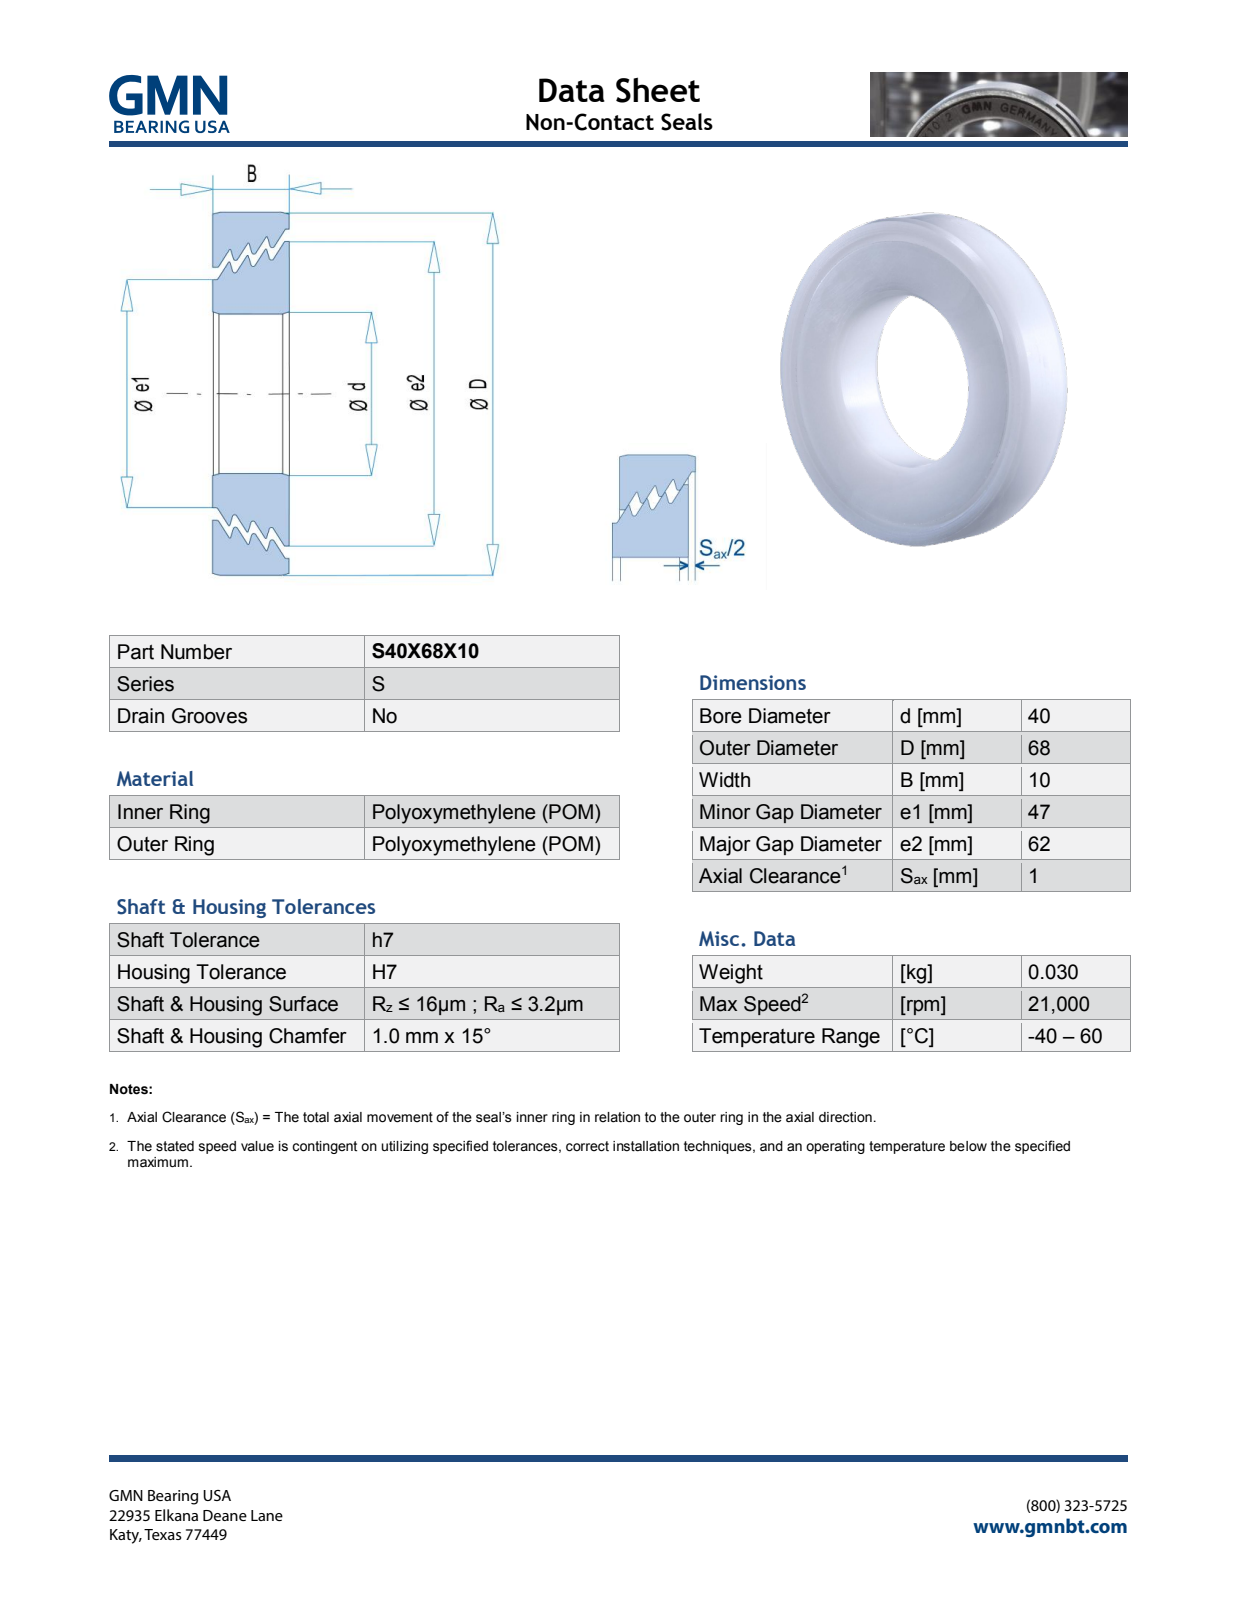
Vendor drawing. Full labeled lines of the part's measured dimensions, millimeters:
Part name (STEP PRODUCT): S40X68X10_PRT
STEP written by: PRO/ENGINEER BY PARAMETRIC TECHNOLOGY CORPORATION, 2013150 (AUTOMOTIVE_DESIGN)
Units: millimetres
Bodies: 2 solids, 686 faces (606 planar, 12 cylindrical, 68 other)
Overall size (bounding box): 68 × 68 × 10.07
Volume: 22 246 mm³ · Surface area: 14 607 mm²
Round holes (diameter × count): ⌀40 ×1, ⌀48.63 ×1, ⌀63.63 ×1
Round bosses / shafts (diameter × count): ⌀68 ×1, ⌀62 ×1, ⌀47 ×1
Main face-to-face distances: 10, 10.07, 0.38, 3.03, 2.65, 0.37, 0.39, 0.32, 0.34, 1.29
